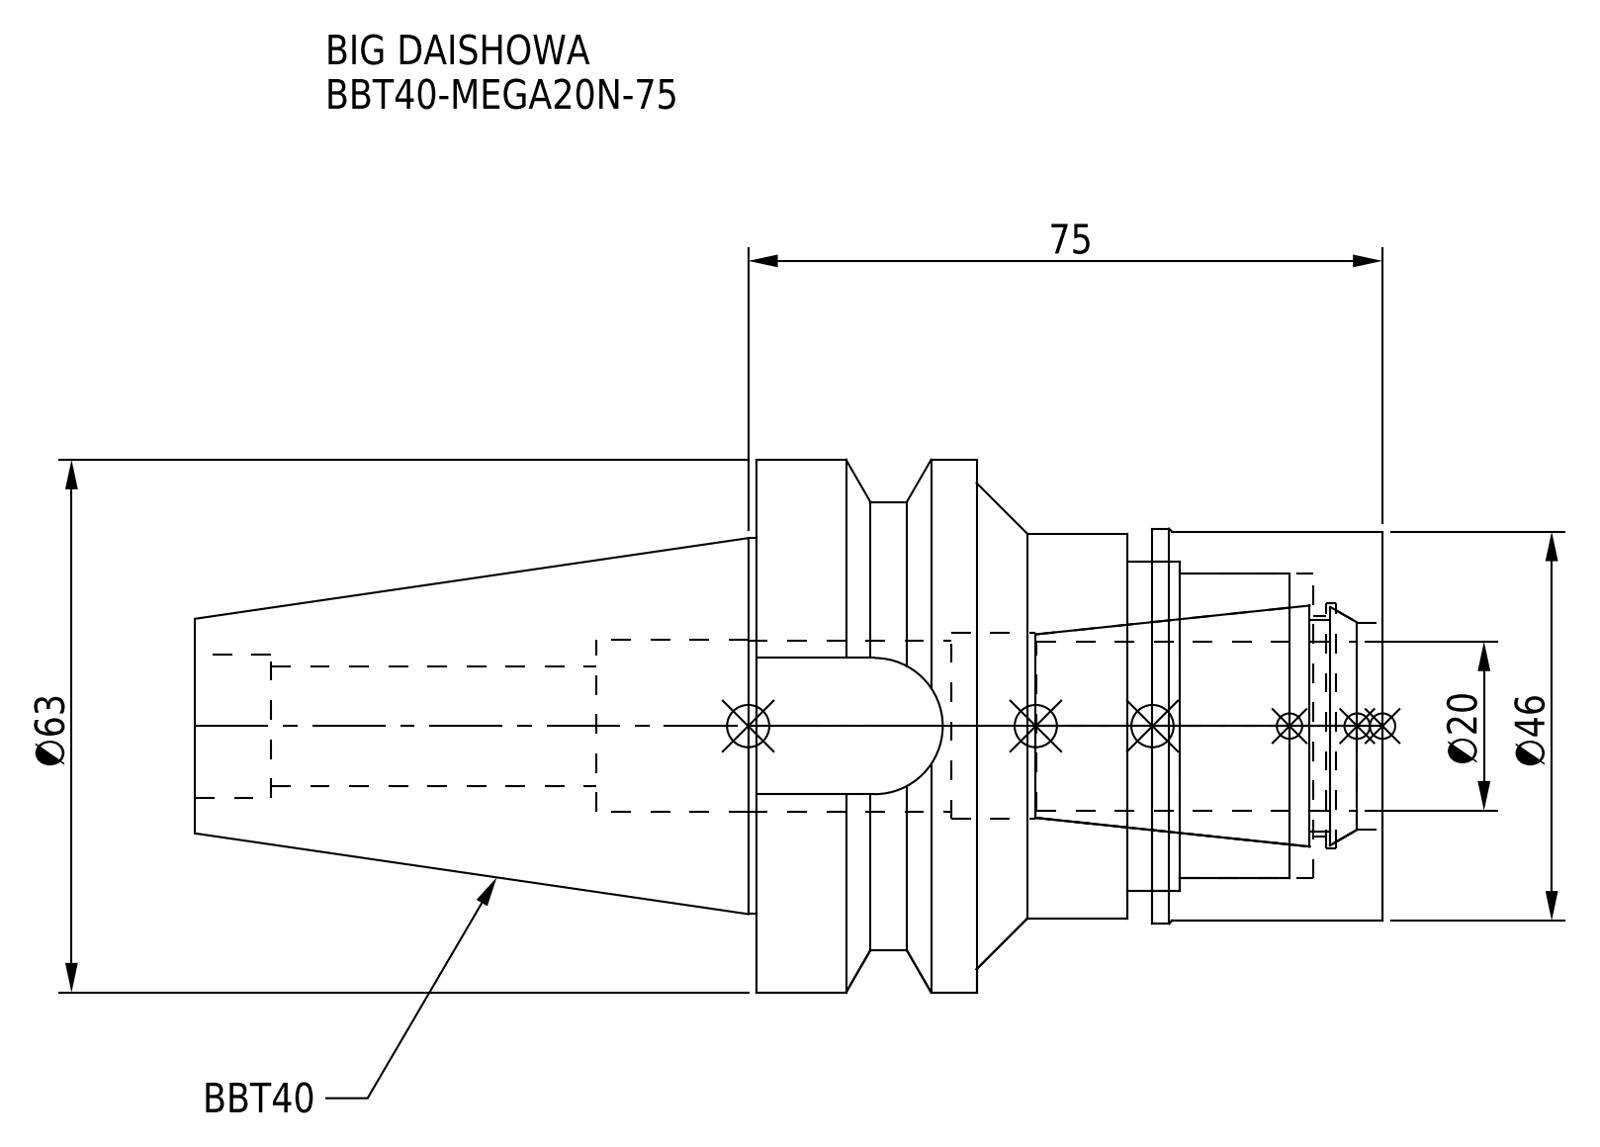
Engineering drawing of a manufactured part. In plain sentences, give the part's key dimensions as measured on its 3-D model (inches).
The part is named "BBT40-MEGA20N-75_1.stp; DXF_TEMP_ASSY_ASM_4_ASM.stp; MGN20_1.stp; BBT40-MEGA20N-75-200-FreeParts (+3 more)". Its 3-D file was written by "SolidWorks 2019 (CONFIG_CONTROL_DESIGN)". It is 2 solids with 76 faces: 22 planar, 40 cylindrical and 14 other. Overall it measures 5.528 by 2.48 by 2.48 inches. Its volume is 10.31 cubic inches and its surface area 61.87 square inches. Round holes: 1 of diameter 0.559, 1 of diameter 0.669, 1 of diameter 0.799, 1 of diameter 0.8, 1 of diameter 0.866, 1 of diameter 0.965, 1 of diameter 1.024, 1 of diameter 1.142, 1 of diameter 1.417, 1 of diameter 1.535. Round bosses or shafts: 1 of diameter 2.48, 1 of diameter 2.087, 1 of diameter 1.839, 1 of diameter 1.811, 1 of diameter 1.791, 1 of diameter 1.75. Partial cylindrical surfaces (rounded edges, fillets, slot ends): 1 of radius 0.317. The main face-to-face distances are 2.913, 0.945, 0.748, 2.591, 0.819, 1.89, 1.024, 1.071, 1.843, 1.772.
